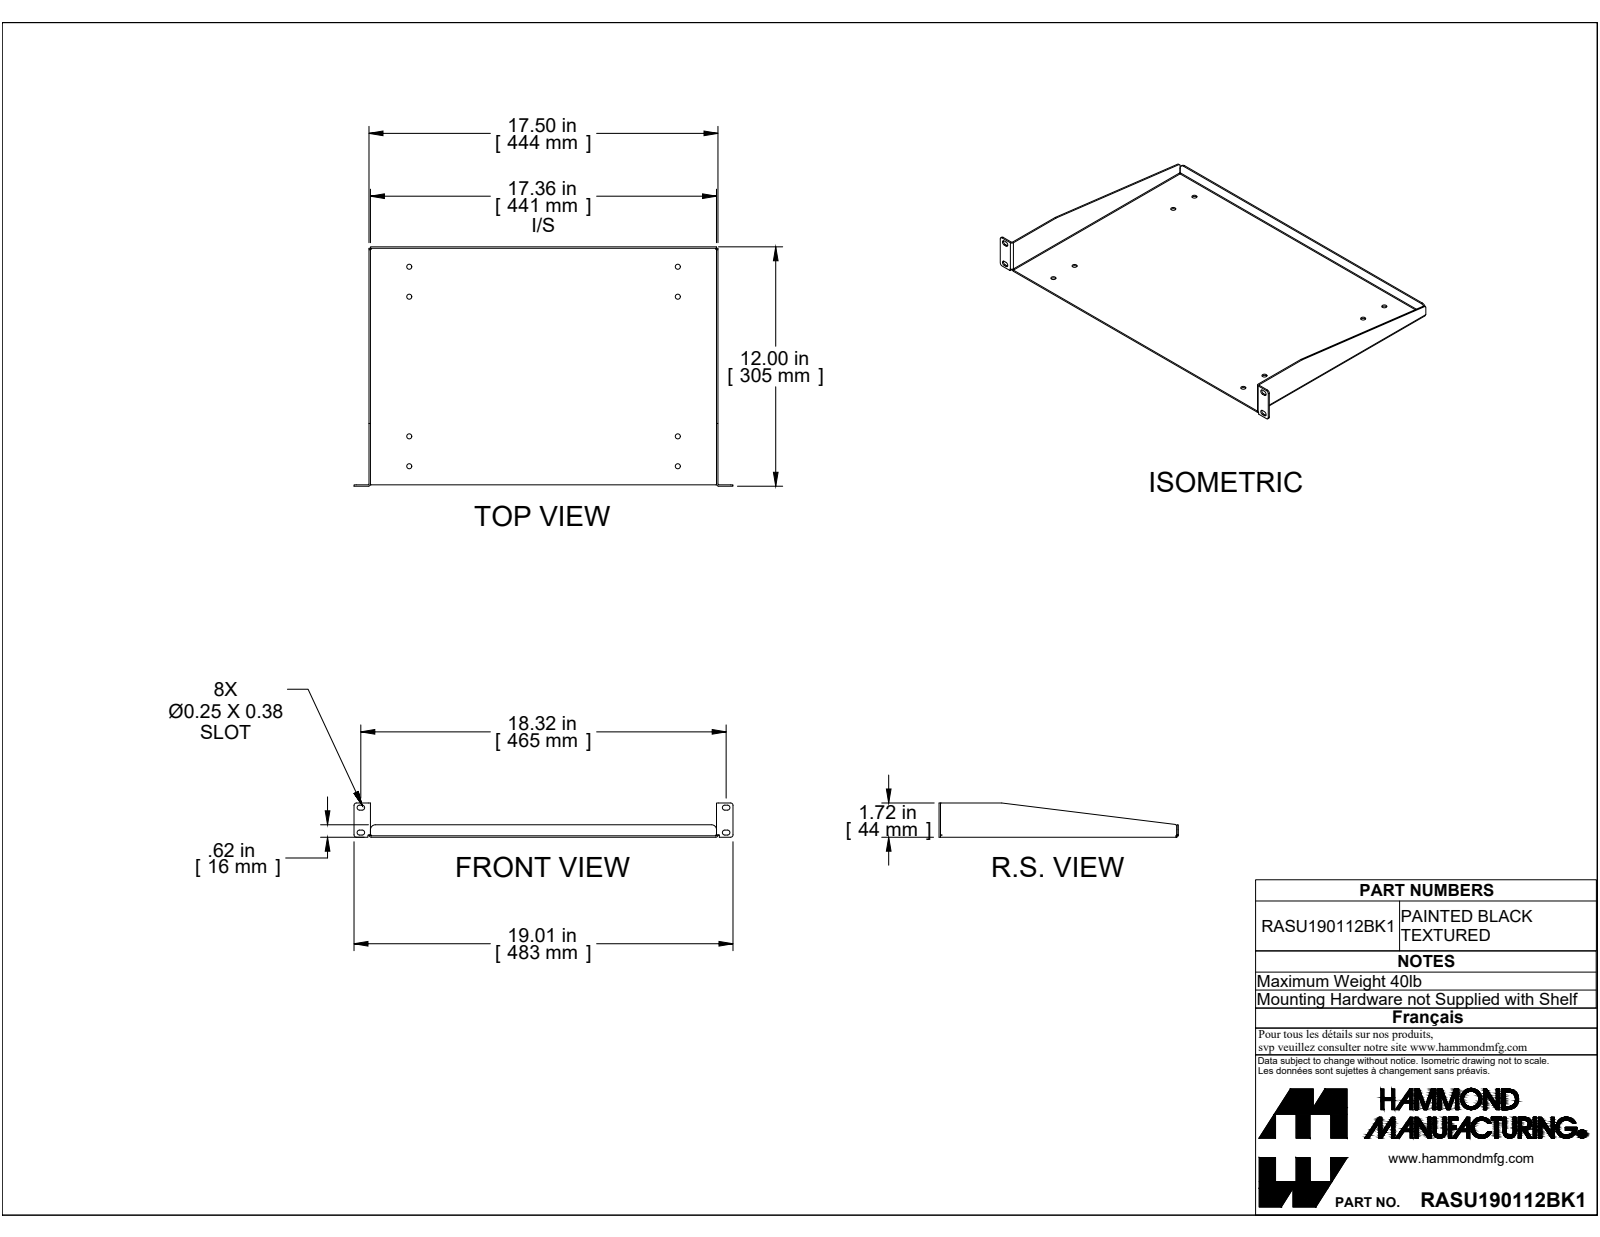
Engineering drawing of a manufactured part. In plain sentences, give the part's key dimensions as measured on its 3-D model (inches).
The part is named "RASU190112BK1". Its 3-D file was written by "SolidWorks 2019 (CONFIG_CONTROL_DESIGN)". It is 1 solid with 88 faces: 48 planar, 36 cylindrical and 4 other. Overall it measures 19.006 by 12 by 1.718 inches. Its volume is 17.89 cubic inches and its surface area 502.6 square inches. Round holes: 8 of diameter 0.25. Partial cylindrical surfaces (rounded edges, fillets, slot ends): 12 of radius 0.125, 5 of radius 0.036, 5 of radius 0.108, 3 of radius 0.055, 2 of radius 0.25. The main face-to-face distances are 0.072, 17.428, 17.356, 17.5, 11.856, 11.928, 0.072, 11.928, 12, 0.625. The hole center spacings are 1.5, 8.5, 13.468, 13.551, 15.926, 7, 10, 15.178.
